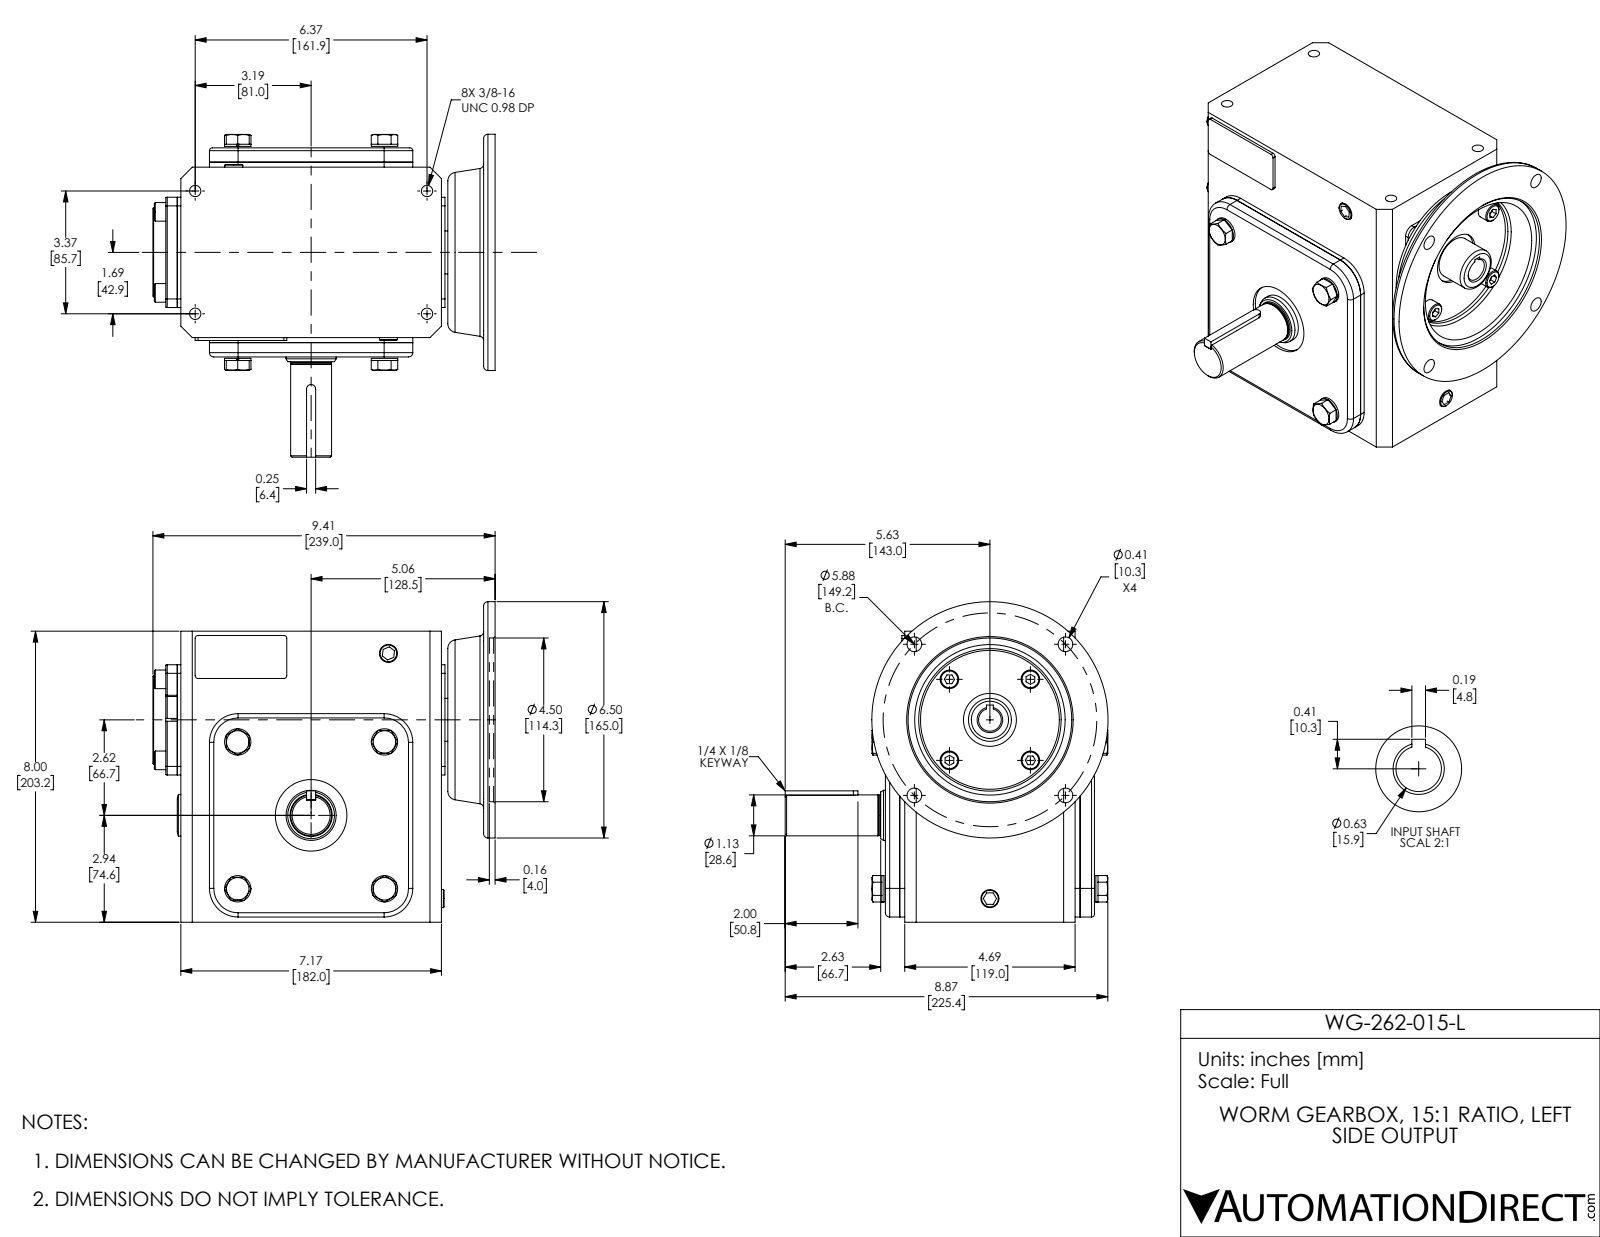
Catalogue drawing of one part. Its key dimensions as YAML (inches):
part_name: "WG-262-015-L"
step_written_by: "SolidWorks 2017 (AUTOMOTIVE_DESIGN)"
units: inches
bodies: {solids: 37, faces: 536, planar: 293, cylindrical: 145, other: 98}
overall_size: [9.409, 8.878, 8.811]
volume: 318.1
surface_area: 613.7
round_holes:
  - {diameter: 0.313, count: 4}
  - {diameter: 0.406, count: 4}
  - {diameter: 0.591, count: 1}
  - {diameter: 0.625, count: 1}
  - {diameter: 1.181, count: 1}
  - {diameter: 1.378, count: 1}
  - {diameter: 1.457, count: 1}
  - {diameter: 1.969, count: 1}
  - {diameter: 3.819, count: 1}
  - {diameter: 4.5, count: 1}
round_bosses_or_shafts:
  - {diameter: 0.724, count: 4}
  - {diameter: 0.512, count: 4}
  - {diameter: 6.496, count: 1}
  - {diameter: 2.441, count: 1}
  - {diameter: 2.047, count: 1}
  - {diameter: 1.142, count: 1}
  - {diameter: 1.125, count: 1}
  - {diameter: 1.113, count: 1}
partial_cylinders:
  - {radius: 0.079, count: 12}
  - {radius: 0.118, count: 4}
  - {radius: 0.236, count: 4}
  - {radius: 0.787, count: 4}
  - {radius: 0.02, count: 2}
  - {radius: 0.039, count: 2}
  - {radius: 0.125, count: 1}
face_to_face_distances: [0.394, 4.961, 5.354, 0.531, 5.217, 0.138, 4.823, 8, 0.098, 7.264]
hole_center_spacings: [2.937, 4.154, 2.148, 3.375, 5.14, 5.875, 6.375, 7.213]
